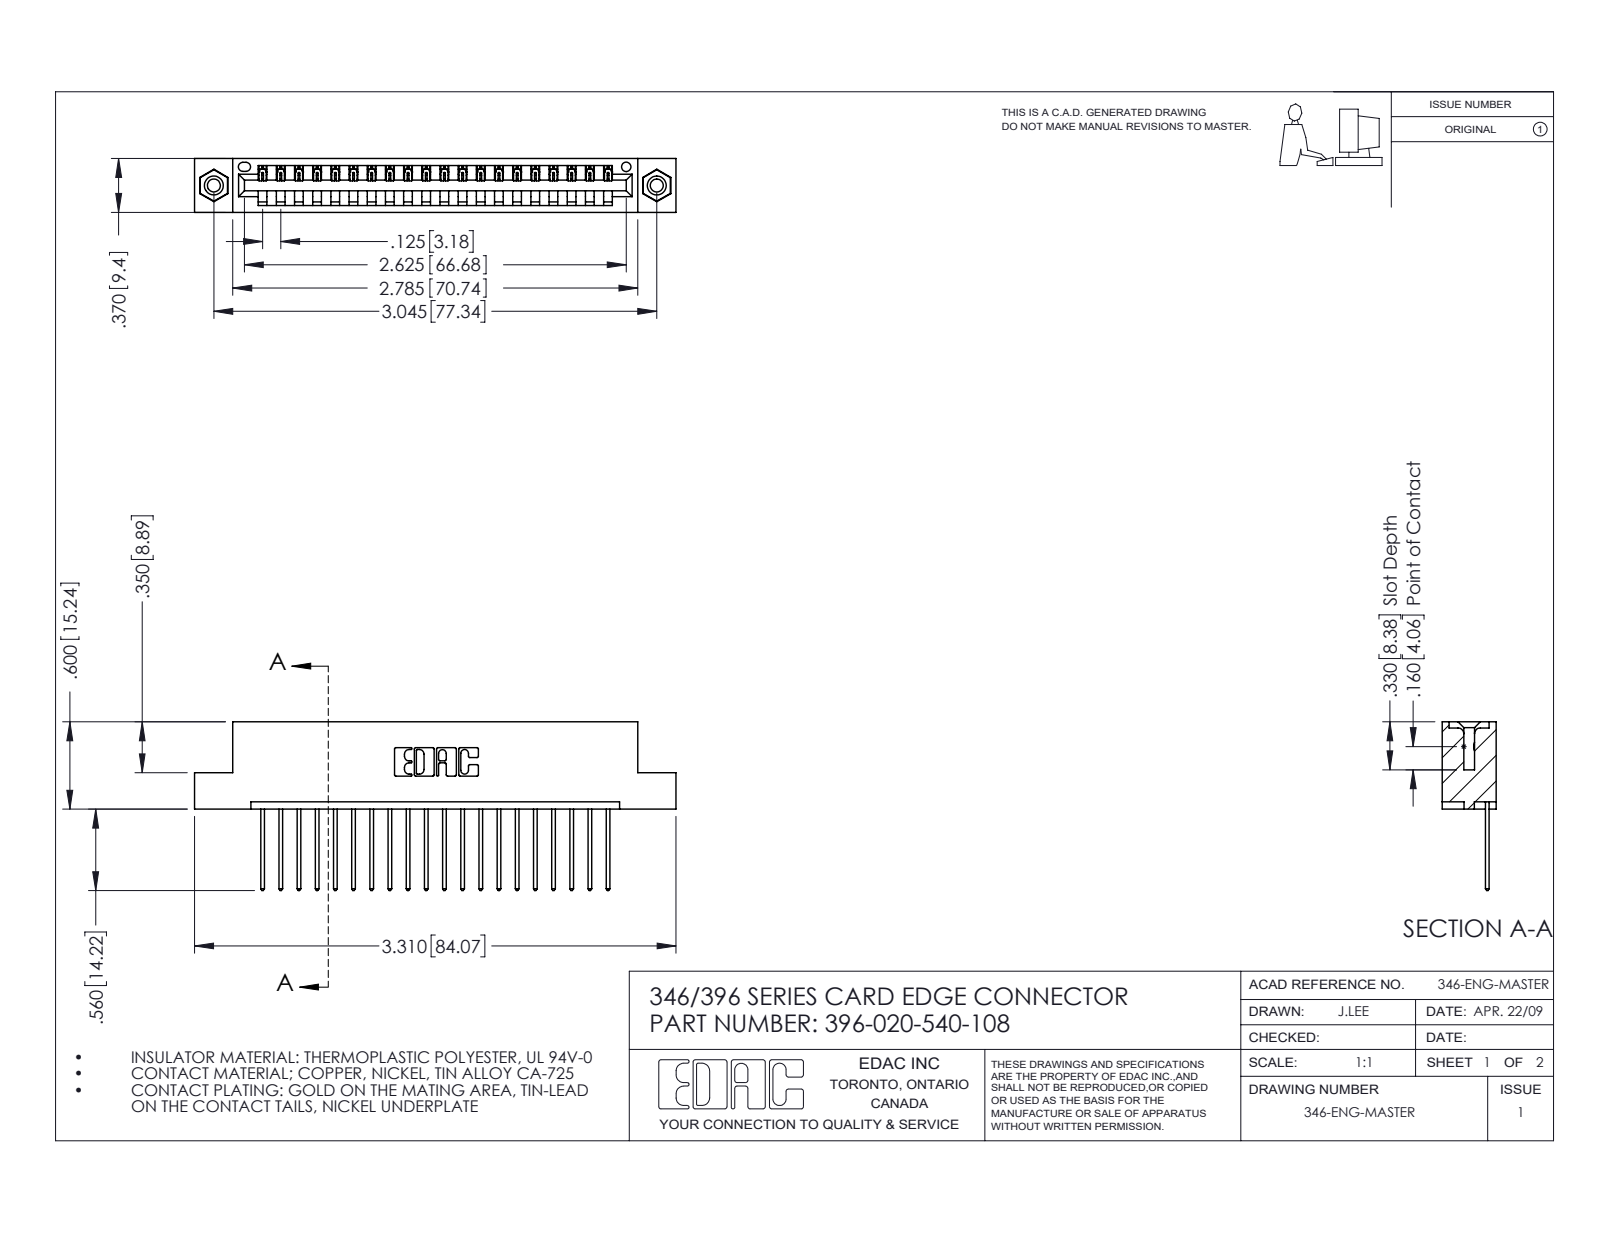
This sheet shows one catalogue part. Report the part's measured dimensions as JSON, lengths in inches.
{"part_name": "345-250-001_345-250-003-102; 345-292-001_345-293-140; 346 Part_Flush Mounting Lugs - 0.156 Dia-TI; 396-020-540-108", "step_written_by": "SolidWorks 2016 (CONFIG_CONTROL_DESIGN)", "units": "inches", "bodies": {"solids": 23, "faces": 1342, "planar": 908, "cylindrical": 418, "other": 16}, "overall_size": [3.31, 1.16, 0.37], "volume_in3": 0.483, "surface_area_in2": 15.31, "round_holes": [[0.089, 2], [0.125, 2], [0.156, 2], [0.064, 1]], "round_bosses_or_shafts": [[0.155, 2]], "partial_cylinders_radius": [[0.006, 40], [0.01, 40], [0.01, 22], [0.007, 6], [0.031, 6], [0.026, 3], [0.031, 2], [0.04, 2]], "face_to_face_distances": [0.048, 0.322, 0.25, 0.37, 0.072, 0.298, 0.025, 0.148, 0.222, 0.1], "hole_center_spacings": [0.246, 2.837, 3.045]}
